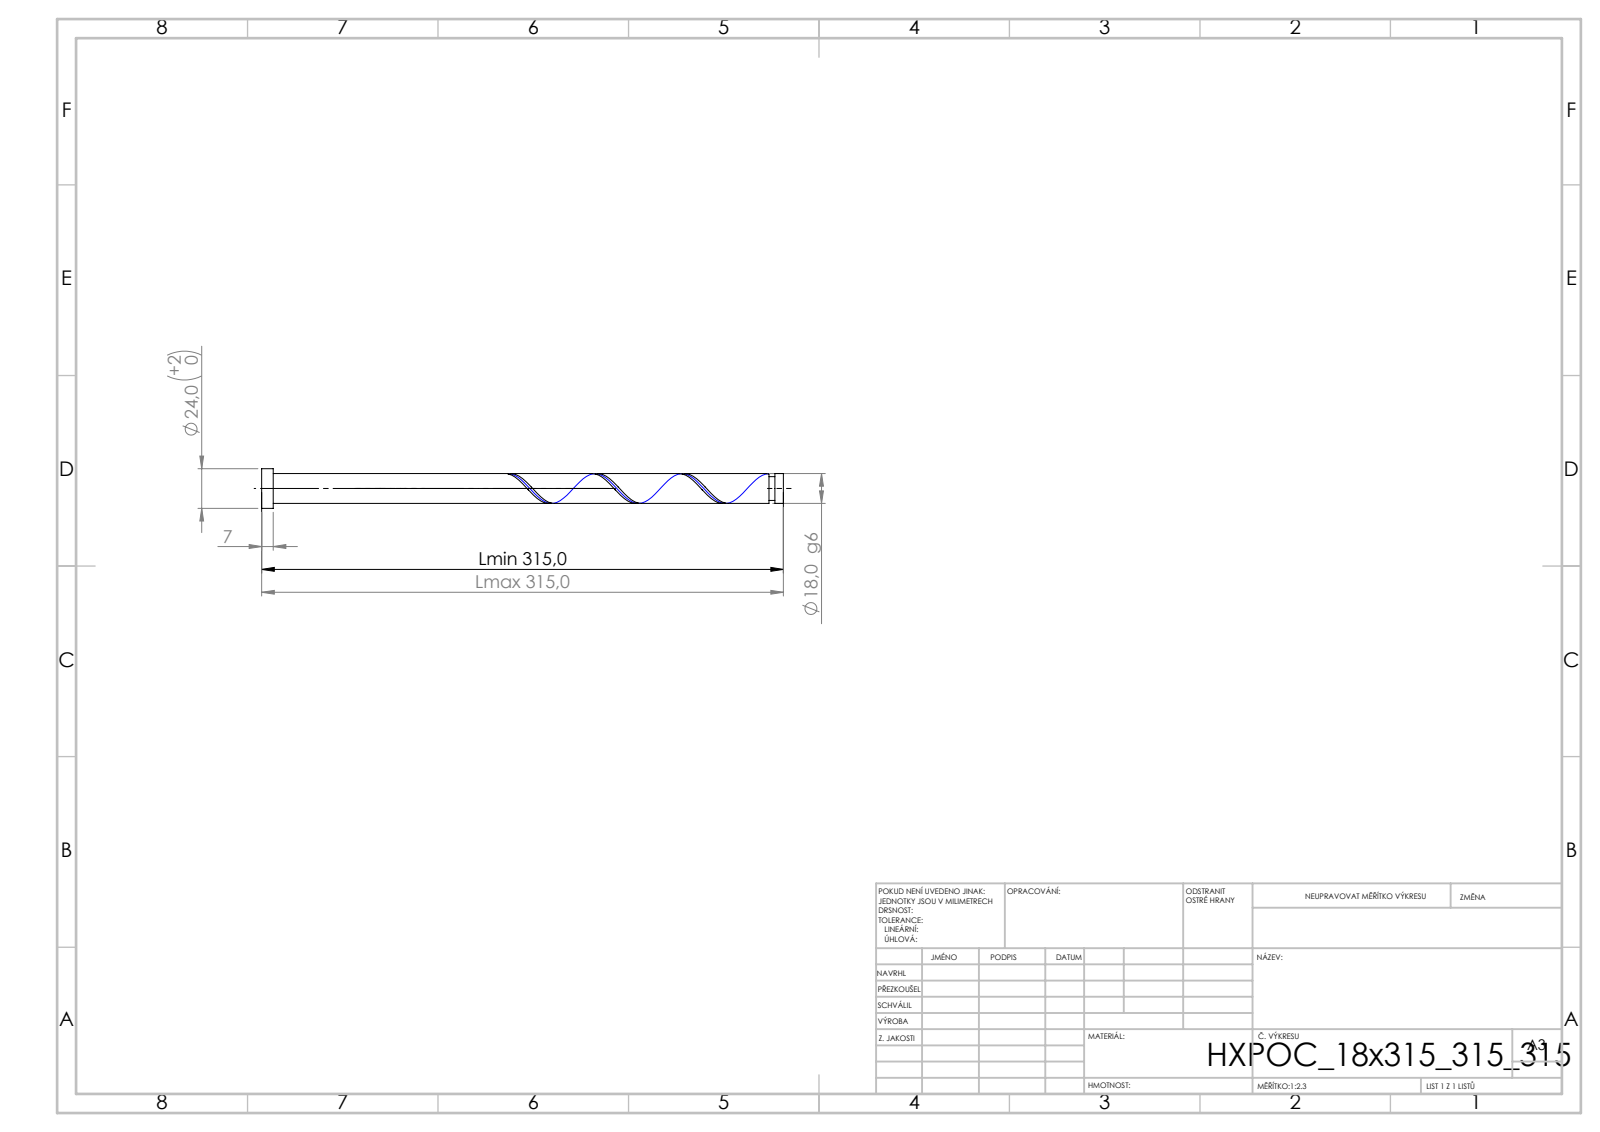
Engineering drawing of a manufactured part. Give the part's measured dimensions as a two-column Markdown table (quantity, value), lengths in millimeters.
| quantity | value |
| --- | --- |
| STEP written by | SolidWorks 2019 (CONFIG_CONTROL_DESIGN) |
| units | millimeters |
| bodies | 1 solid, 21 faces (6 planar, 14 cylindrical, 1 other) |
| overall size | 315 × 24 × 24 |
| volume | 80 446 mm³ |
| surface area | 19 450 mm² |
| round bosses / shafts (diameter × count) | 24 × 1, 18 × 1, 14.4 × 1 |
| main face-to-face distances | 315, 7, 308, 309.89, 302.89, 5.11, 306.29, 299.29, 3.6, 8.71 |
